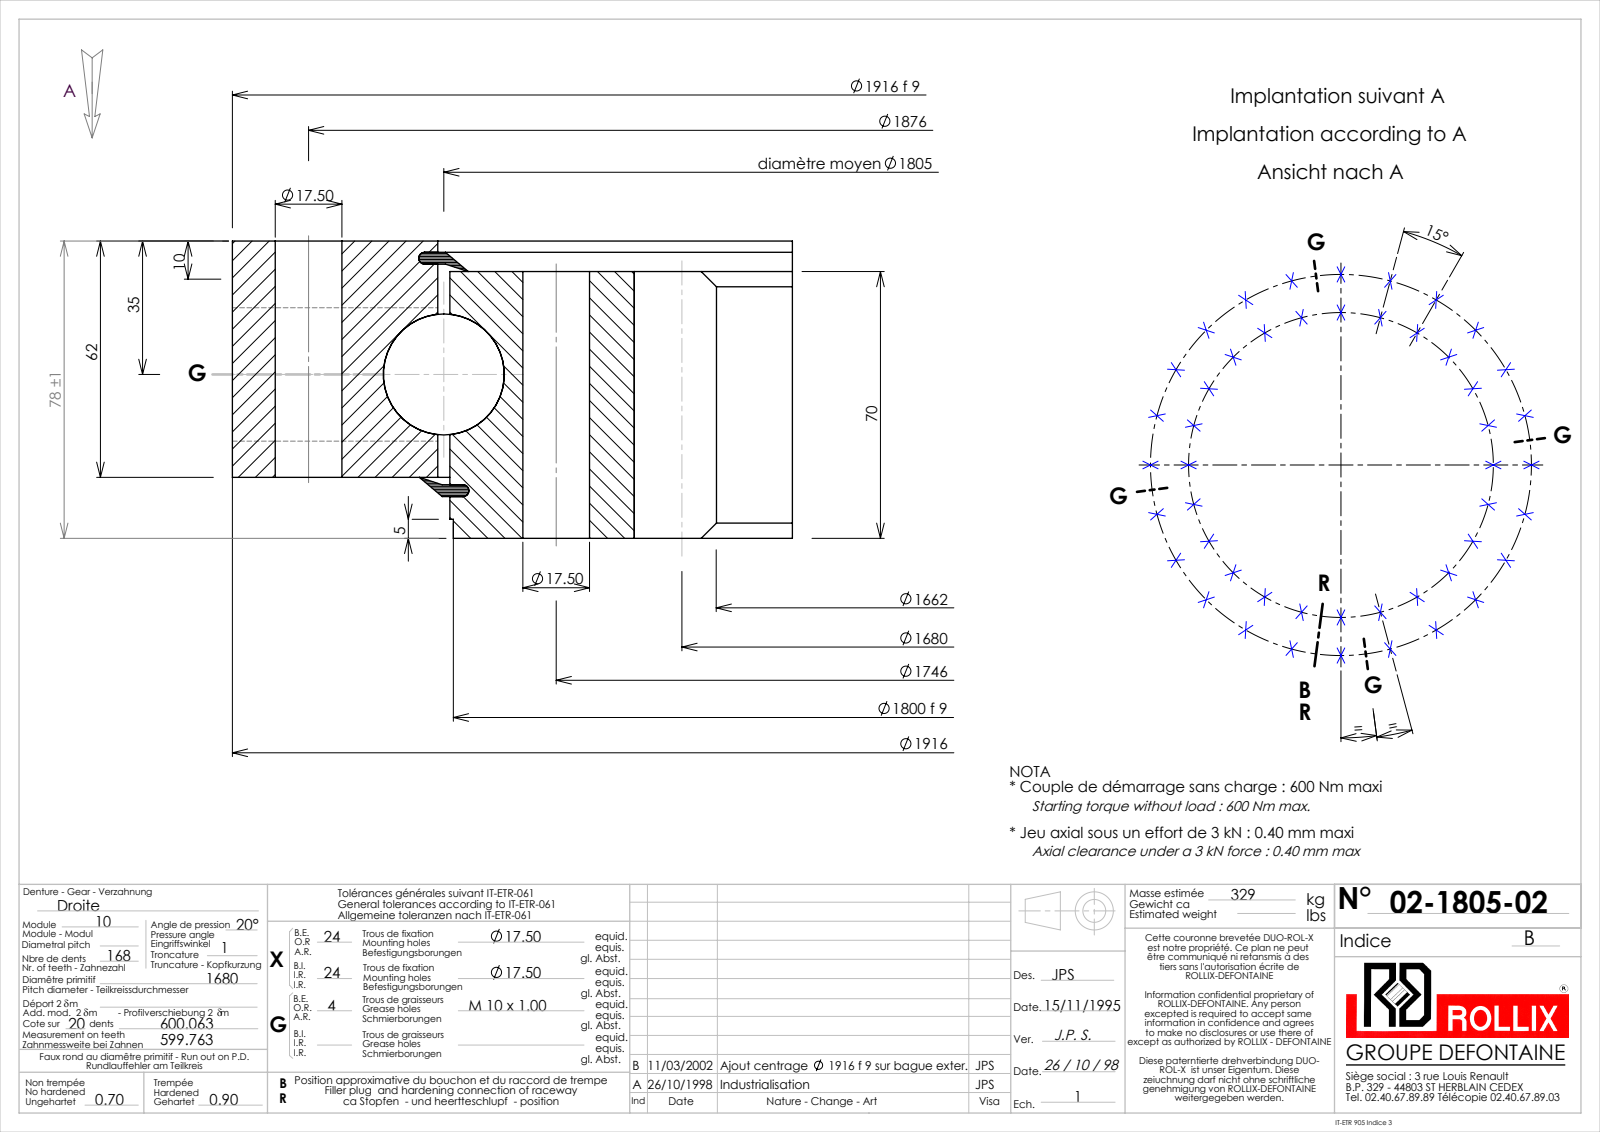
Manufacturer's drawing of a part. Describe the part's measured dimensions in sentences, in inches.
The part is named "02-1805-02". Its 3-D file was written by "SolidWorks 2016 (CONFIG_CONTROL_DESIGN)". It is 5 solids with 1170 faces: 349 planar, 457 cylindrical and 364 other. Overall it measures 75.433 by 75.433 by 3.071 inches. Its volume is 2 318 cubic inches and its surface area 6 022 square inches. Round holes: 48 of diameter 0.689, 4 of diameter 0.354, 1 of diameter 71.188. Round bosses or shafts: 1 of diameter 75.433, 1 of diameter 70.938, 1 of diameter 70.866. Partial cylindrical surfaces (rounded edges, fillets, slot ends): 1 of radius 32.717, 1 of radius 33.563. The main face-to-face distances are 2.756, 3.071, 0.315, 0.63, 2.126, 2.441, 0.077, 2.203, 0.122, 0.199. The hole center spacings are 8.972, 54.535, 63.507, 68.152, 34.37, 17.791, 26.306, 41.846.
